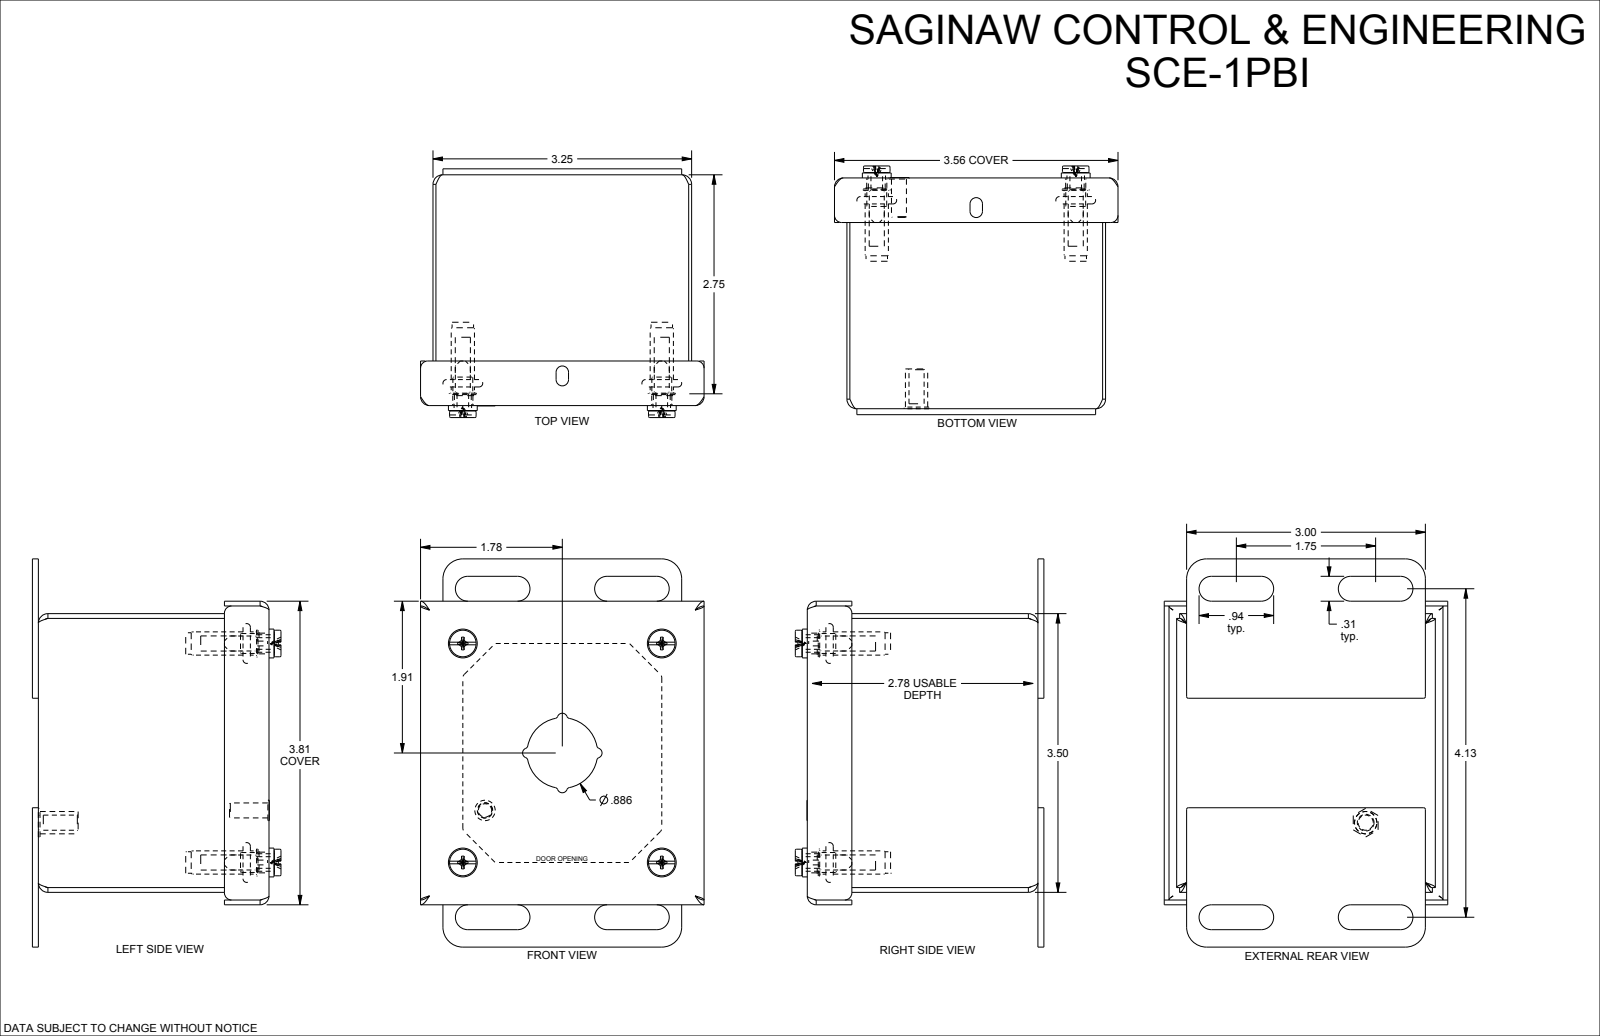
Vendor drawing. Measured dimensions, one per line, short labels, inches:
name: SCE-1PBI
written by: SolidWorks 2021 (AUTOMOTIVE_DESIGN)
unit: in
bodies: 15 solids, 426 faces (162 planar, 188 cylindrical, 76 other)
size: 4.875 × 3.562 × 3.036
volume: 5.331 in³; area: 177.6 in²
holes: 5× ⌀0.19, 4× ⌀0.22, 4× ⌀0.25, 4× ⌀0.266, 4× ⌀0.317
bosses: 4× ⌀0.362, 4× ⌀0.34, 4× ⌀0.292, 4× ⌀0.27, 4× ⌀0.26, 1× ⌀0.28, 1× ⌀0.256, 1× ⌀0.188
rounds: 12× R0.06, 12× R0.12, 8× R0.015, 8× R0.04, 8× R0.06, 8× R0.115, 8× R0.156, 8× R0.245
face distances: 0.06, 2.838, 3.19, 3.44, 2.898, 2.778, 0.075, 0.135, 2.913, 2.973
hole spacings: 2.5, 3.717, 2.5, 2.5, 2.75, 2.75, 3.715, 3.716
